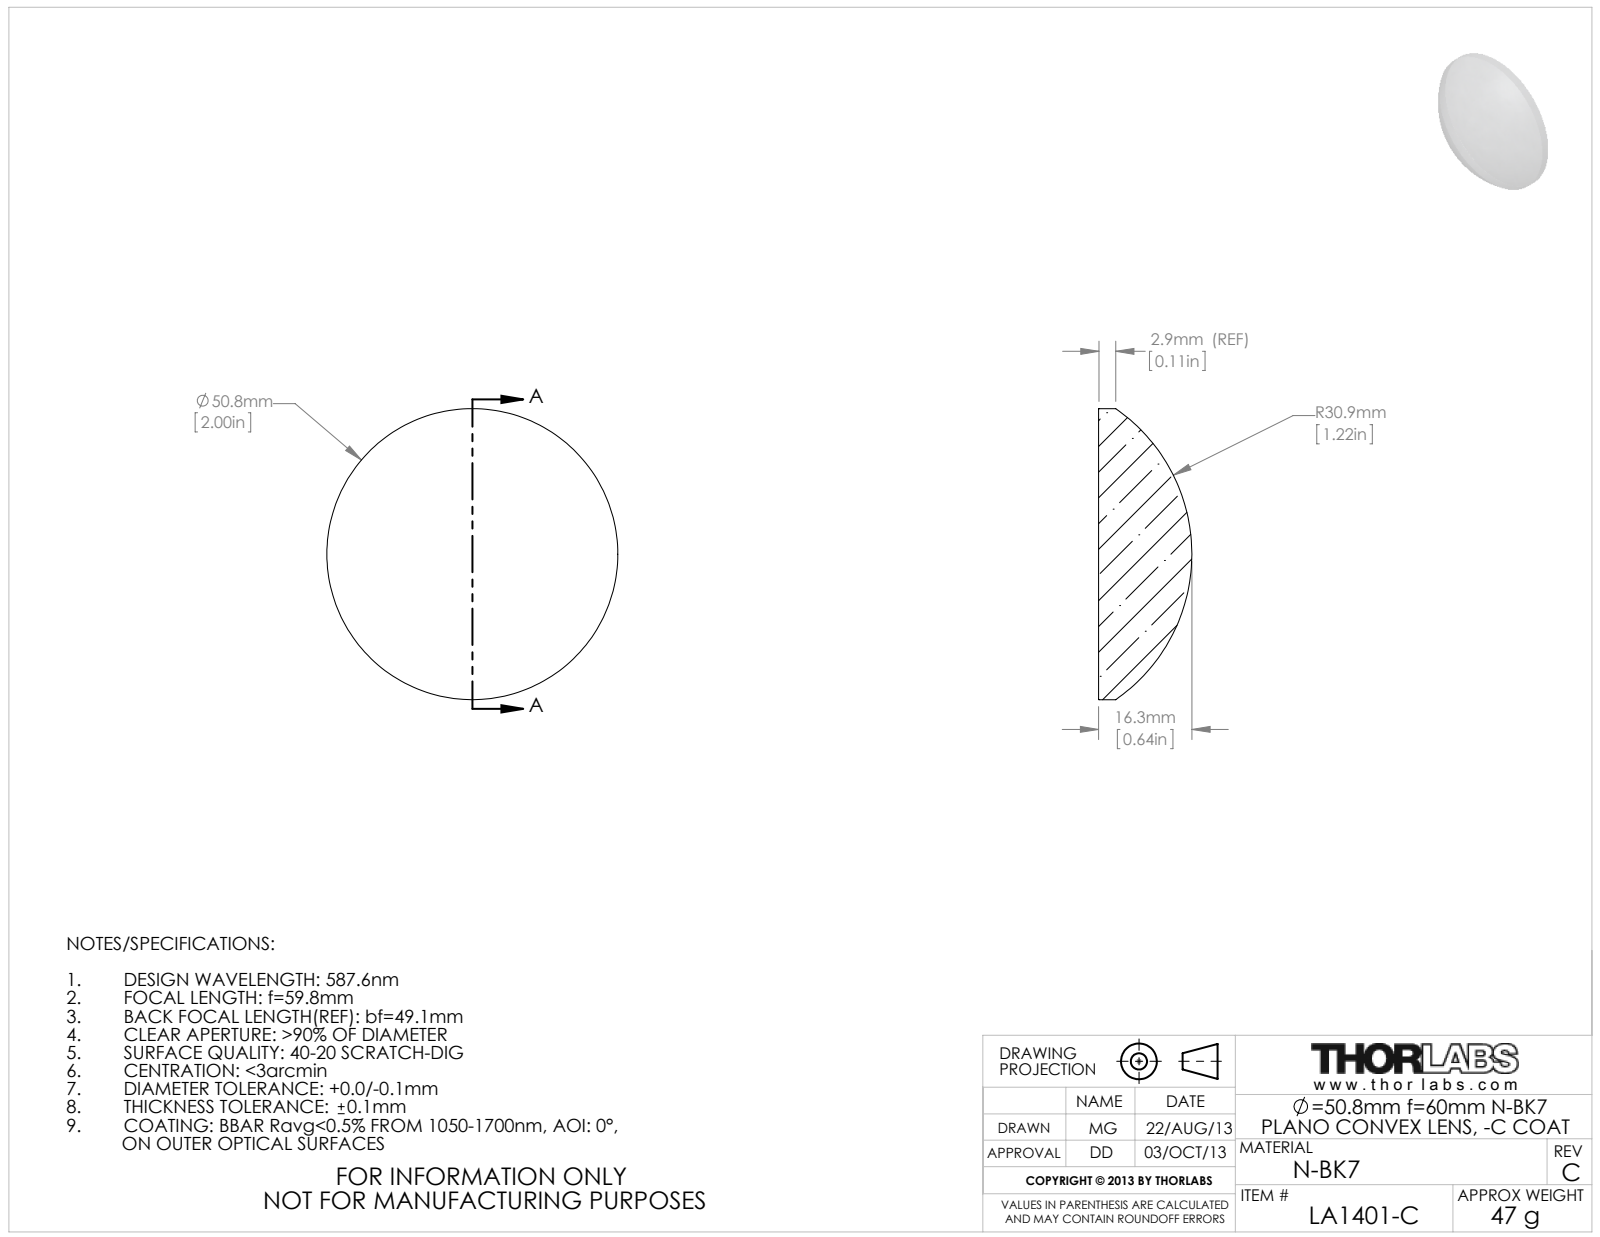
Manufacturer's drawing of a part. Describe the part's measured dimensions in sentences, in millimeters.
The part is named "4600-E0W". Its 3-D file was written by "SolidWorks 2009 (AUTOMOTIVE_DESIGN)". It is 0 solids with 5 faces: 1 planar, 2 cylindrical and 2 other. Overall it measures 50.8 by 50.8 by 16.29 millimeters. Round bosses or shafts: 1 of diameter 50.8.
